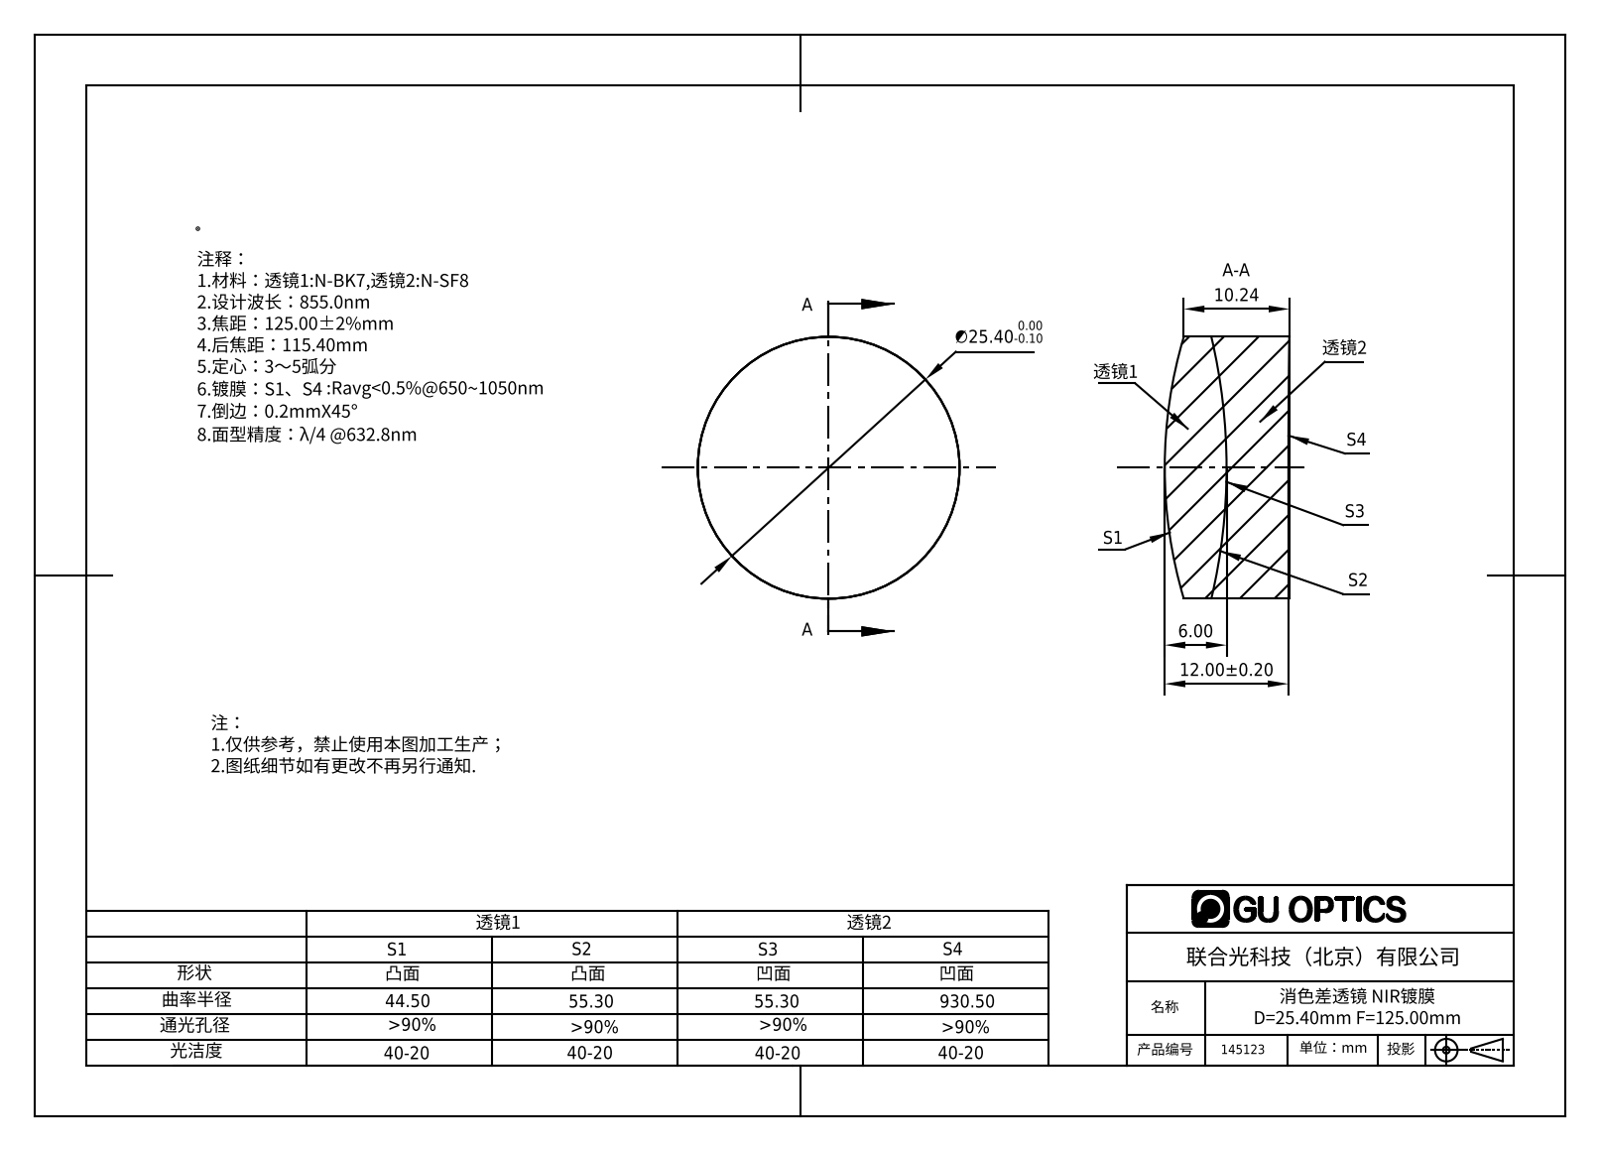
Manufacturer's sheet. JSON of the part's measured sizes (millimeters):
{"part_name": "145123", "step_written_by": "SolidWorks 2016 (AUTOMOTIVE_DESIGN)", "units": "millimeters", "bodies": {"solids": 2, "faces": 12, "planar": 0, "cylindrical": 4, "other": 8}, "overall_size": [25.4, 25.4, 12.09], "volume_mm3": 5637, "surface_area_mm2": 2868, "round_bosses_or_shafts": [[25.4, 1]]}
